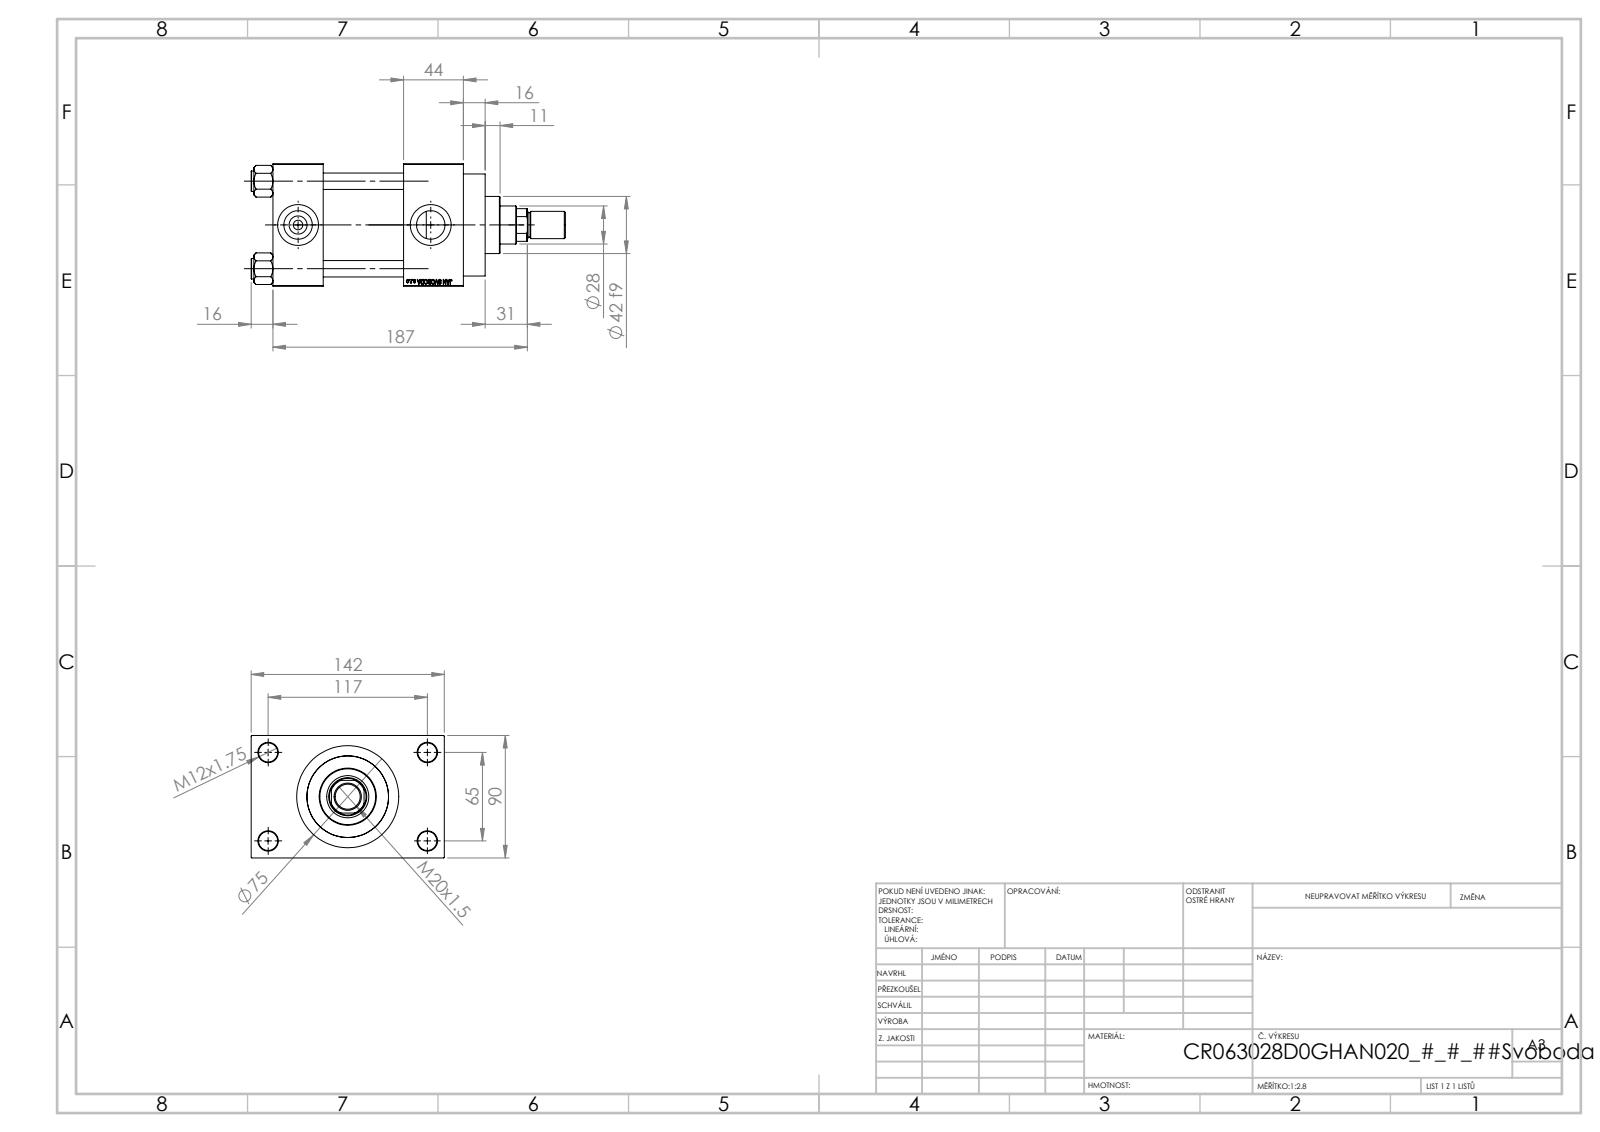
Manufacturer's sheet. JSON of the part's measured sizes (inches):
{"part_name": "NUT_M5_D; V215CR_VCP_D; V215CR_D_Body; V215CR_D_TYCINKA (+2 more)", "step_written_by": "SolidWorks 2019 (CONFIG_CONTROL_DESIGN)", "units": "inches", "bodies": {"solids": 12, "faces": 1117, "planar": 501, "cylindrical": 92, "other": 524}, "overall_size": [9.094, 5.591, 3.543], "volume_in3": 67.43, "surface_area_in2": 314.3, "round_holes": [[0.472, 4], [0.551, 4], [0.276, 2], [0.825, 2], [1.181, 2], [0.728, 1], [1.102, 1], [1.22, 1], [1.969, 1], [2.362, 1], [2.48, 1]], "round_bosses_or_shafts": [[0.591, 4], [2.953, 1], [2.717, 1], [1.654, 1], [0.787, 1], [0.709, 1]], "partial_cylinders_radius": [[0.531, 1]], "face_to_face_distances": [3.543, 2.323, 1.457, 3.78, 5.512, 4.055, 1.732, 1.024, 4.567, 0.63], "hole_center_spacings": [1.037, 1.79, 2.531, 2.635, 2.748, 3.569, 4.383, 2.559]}
